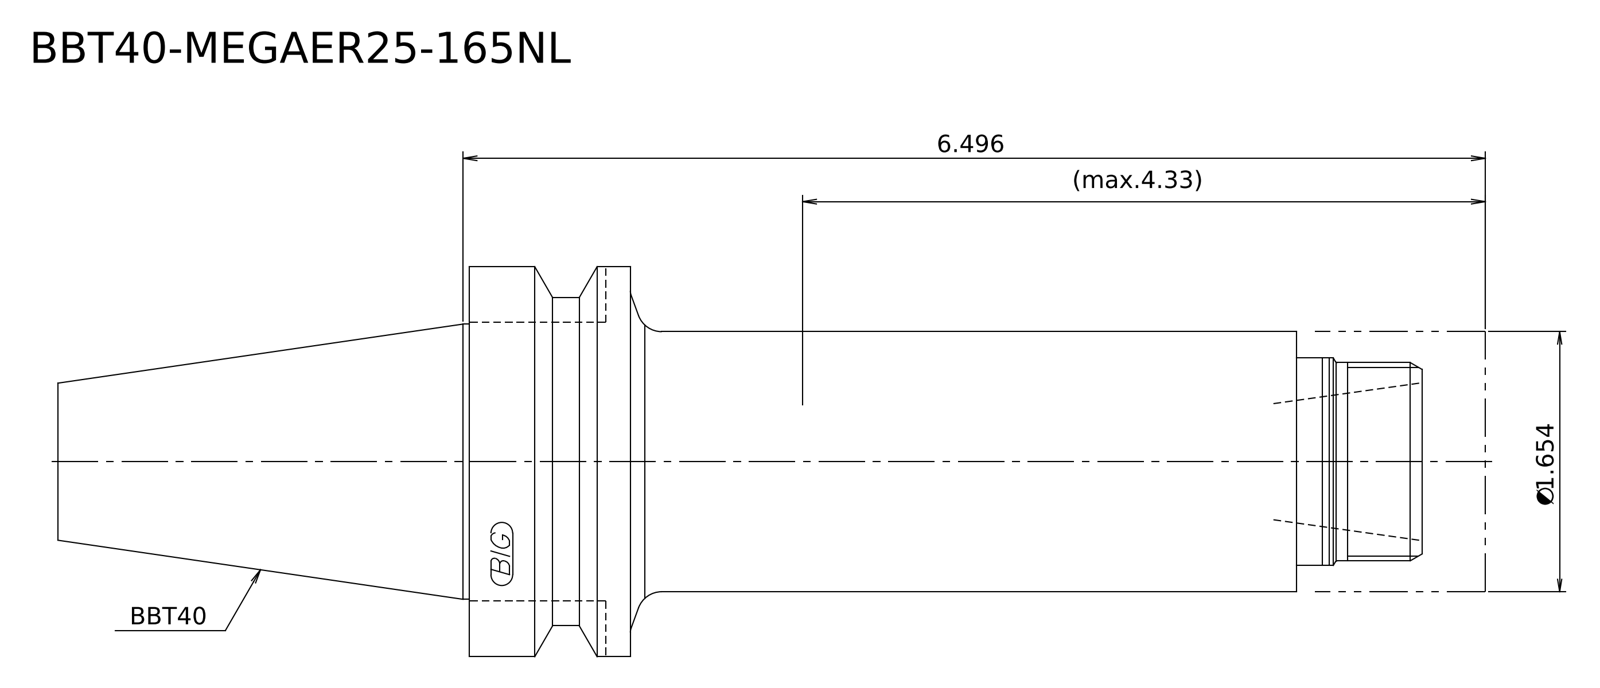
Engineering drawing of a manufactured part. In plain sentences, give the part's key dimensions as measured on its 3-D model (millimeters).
Its 3-D file was written by "Kubotek KeyCreator 2011 V10.0.2 (22737) (automotive_design)". It is 2 solids with 21 faces: 7 planar, 8 cylindrical and 6 other. Overall it measures 230.4 by 63 by 63 millimeters. Its volume is 346 306 cubic millimeters and its surface area 40 681 square millimeters. Round bosses or shafts: 1 of diameter 63, 1 of diameter 53, 1 of diameter 44.45, 1 of diameter 42, 1 of diameter 33.5, 1 of diameter 32. The main face-to-face distances are 136.5, 27.5, 164, 138, 110.5, 26, 10.2, 17.3, 127.8, 153.8.
